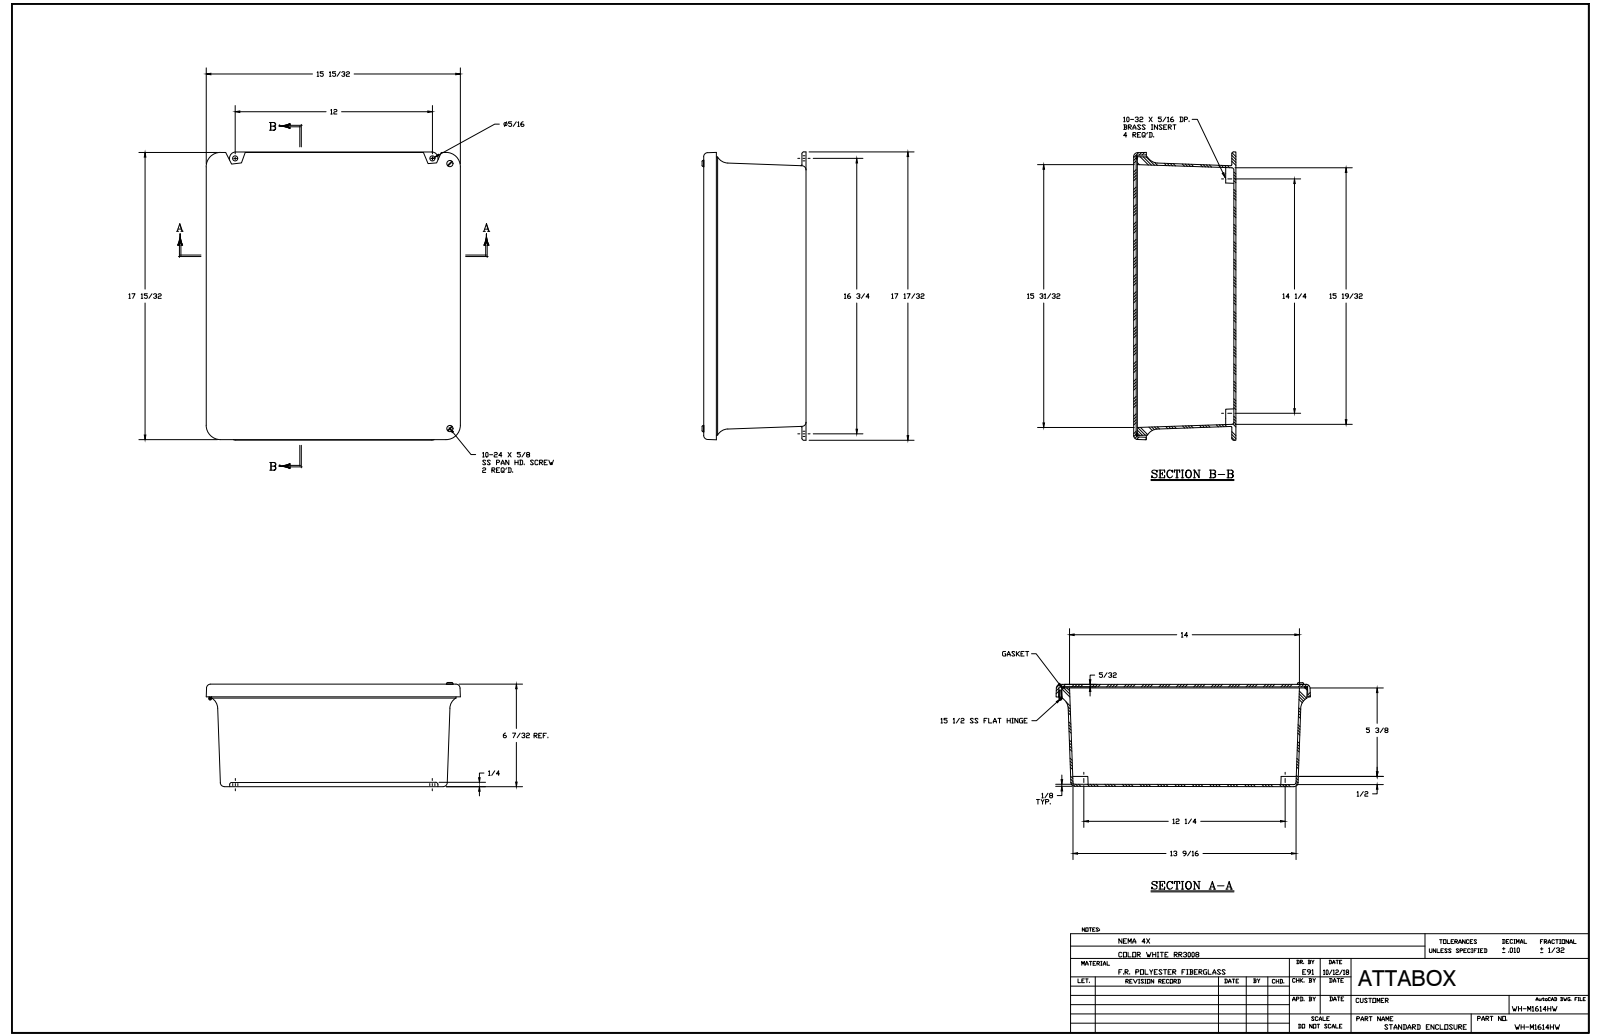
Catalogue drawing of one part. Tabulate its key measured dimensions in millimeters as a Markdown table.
| quantity | value |
| --- | --- |
| part name | WH-M1614HW |
| STEP written by | SolidWorks 2018 (AUTOMOTIVE_DESIGN) |
| units | millimeters |
| bodies | 24 solids, 898 faces (341 planar, 350 cylindrical, 207 other) |
| overall size | 445.3 × 393.4 × 161.4 |
| volume | 2 353 000 mm³ |
| surface area | 1 250 000 mm² |
| round holes (diameter × count) | 3.3 × 10, 3.6 × 10, 3.9 × 8, 4 × 4, 5.5 × 4, 3.7 × 2, 2.2 × 1 |
| round bosses / shafts (diameter × count) | 6.4 × 10, 6.9 × 6, 3.2 × 6, 3.2 × 4, 4.8 × 2, 4 × 2, 3.9 × 1, 3.9 × 1 |
| partial cylindrical surfaces (radius × count) | 0.8 × 20, 3.2 × 12, 6.4 × 12, 5.1 × 5, 9.5 × 4, 19.1 × 4, 1.6 × 2 |
| main face-to-face distances | 3.2, 3.9, 154.2, 158, 151, 154.8, 3.2, 152.4, 149.2, 1.8 |
| hole center spacings | 95.3, 190.5, 285.8, 6.4, 88.9, 33.6, 184.2, 335.8 |
